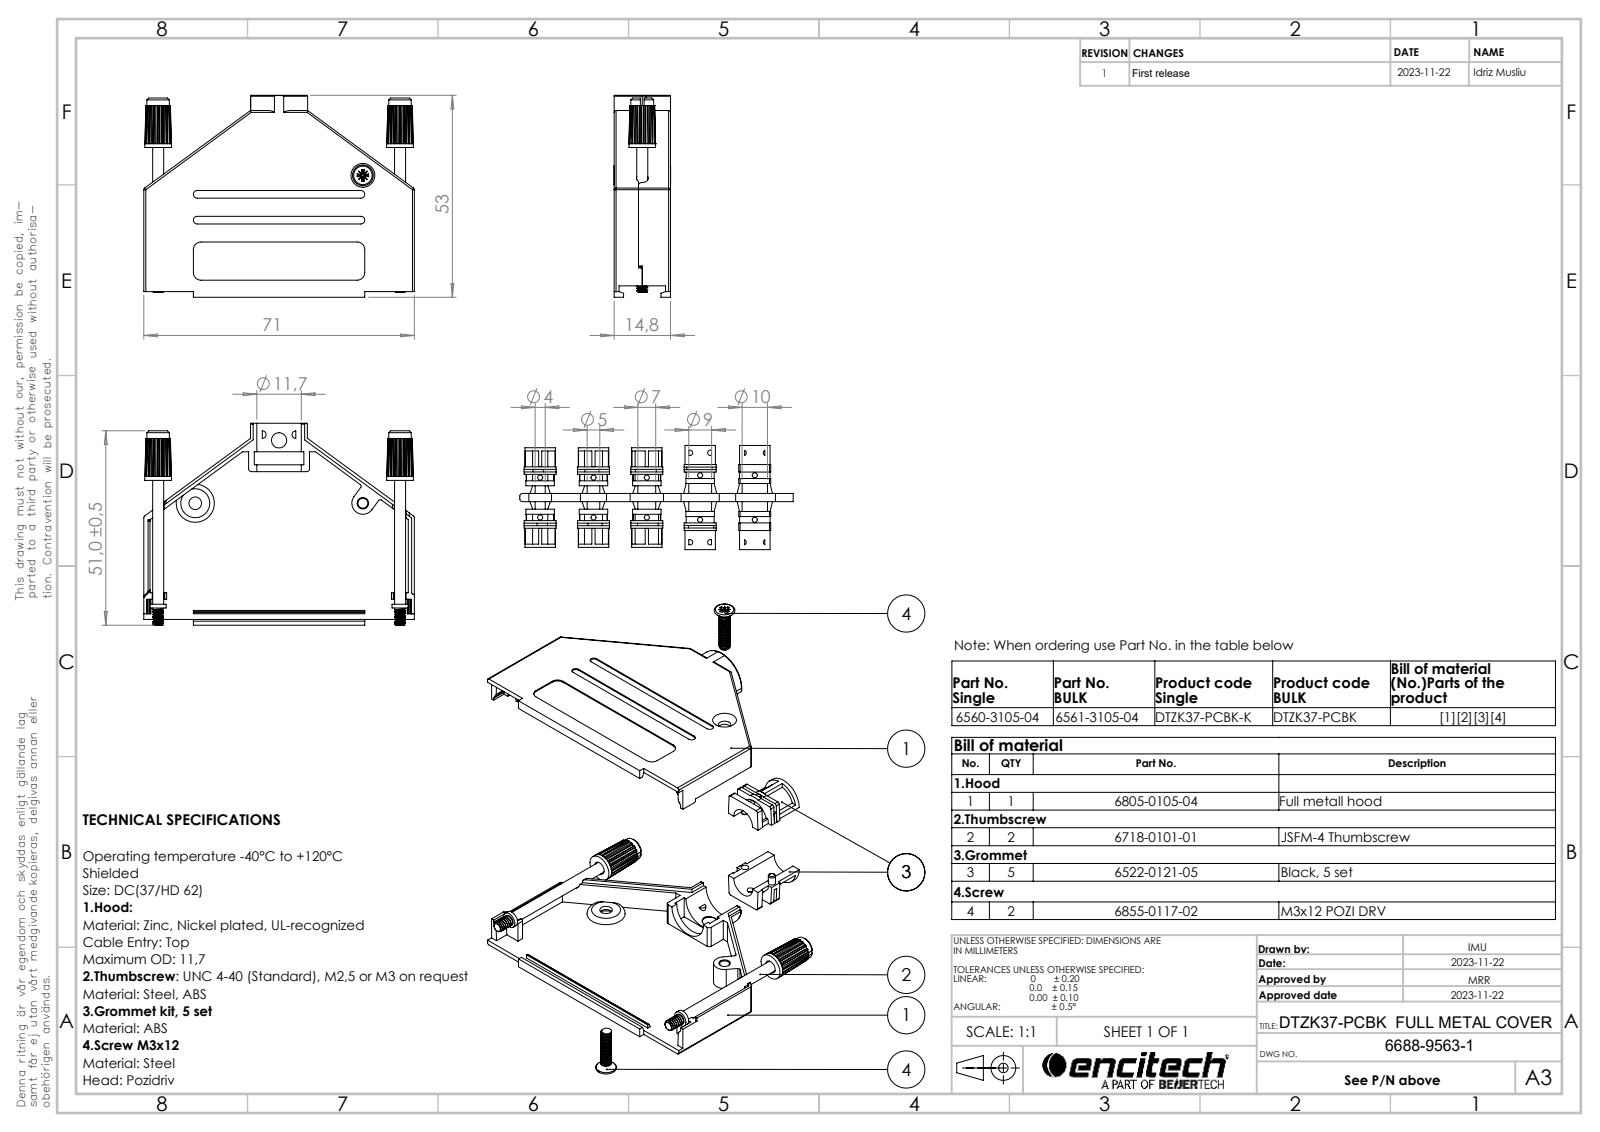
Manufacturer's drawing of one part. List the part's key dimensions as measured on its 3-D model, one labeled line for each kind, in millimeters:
Part name (STEP PRODUCT): 6718-0101-01; 6855-0117-02; 6522-0121-05 (7mm); 6805-0105-04 (+1 more)
STEP written by: SolidWorks 2021 (AUTOMOTIVE_DESIGN)
Units: millimetres
Bodies: 8 solids, 888 faces (520 planar, 260 cylindrical, 108 other)
Overall size (bounding box): 71 × 53 × 14.85
Volume: 13 221 mm³ · Surface area: 20 474 mm²
Round holes (diameter × count): ⌀2 ×3, ⌀2.6 ×2, ⌀3.1 ×2, ⌀3.3 ×2, ⌀4 ×1, ⌀7 ×1, ⌀11.7 ×1
Round bosses / shafts (diameter × count): ⌀2.9 ×4, ⌀7 ×2, ⌀6 ×2, ⌀4.2 ×2, ⌀1.9 ×2, ⌀15 ×1, ⌀11.6 ×1, ⌀9.2 ×1
Partial cylindrical surfaces — rounded edges, fillets, slot ends (radius × count): R0.5 ×32, R1 ×12, R0.1 ×8, R0.25 ×8, R2 ×4, R5.91 ×4, R0.2 ×2, R0.3 ×2
Main face-to-face distances: 1.3, 13.5, 12.2, 14.8, 1, 14.5, 13.2, 6.1, 1.6, 7.1
Hole centre spacings: 5.71, 6.97, 20.61, 23.73, 27.5, 29.41, 31.75, 7.6
